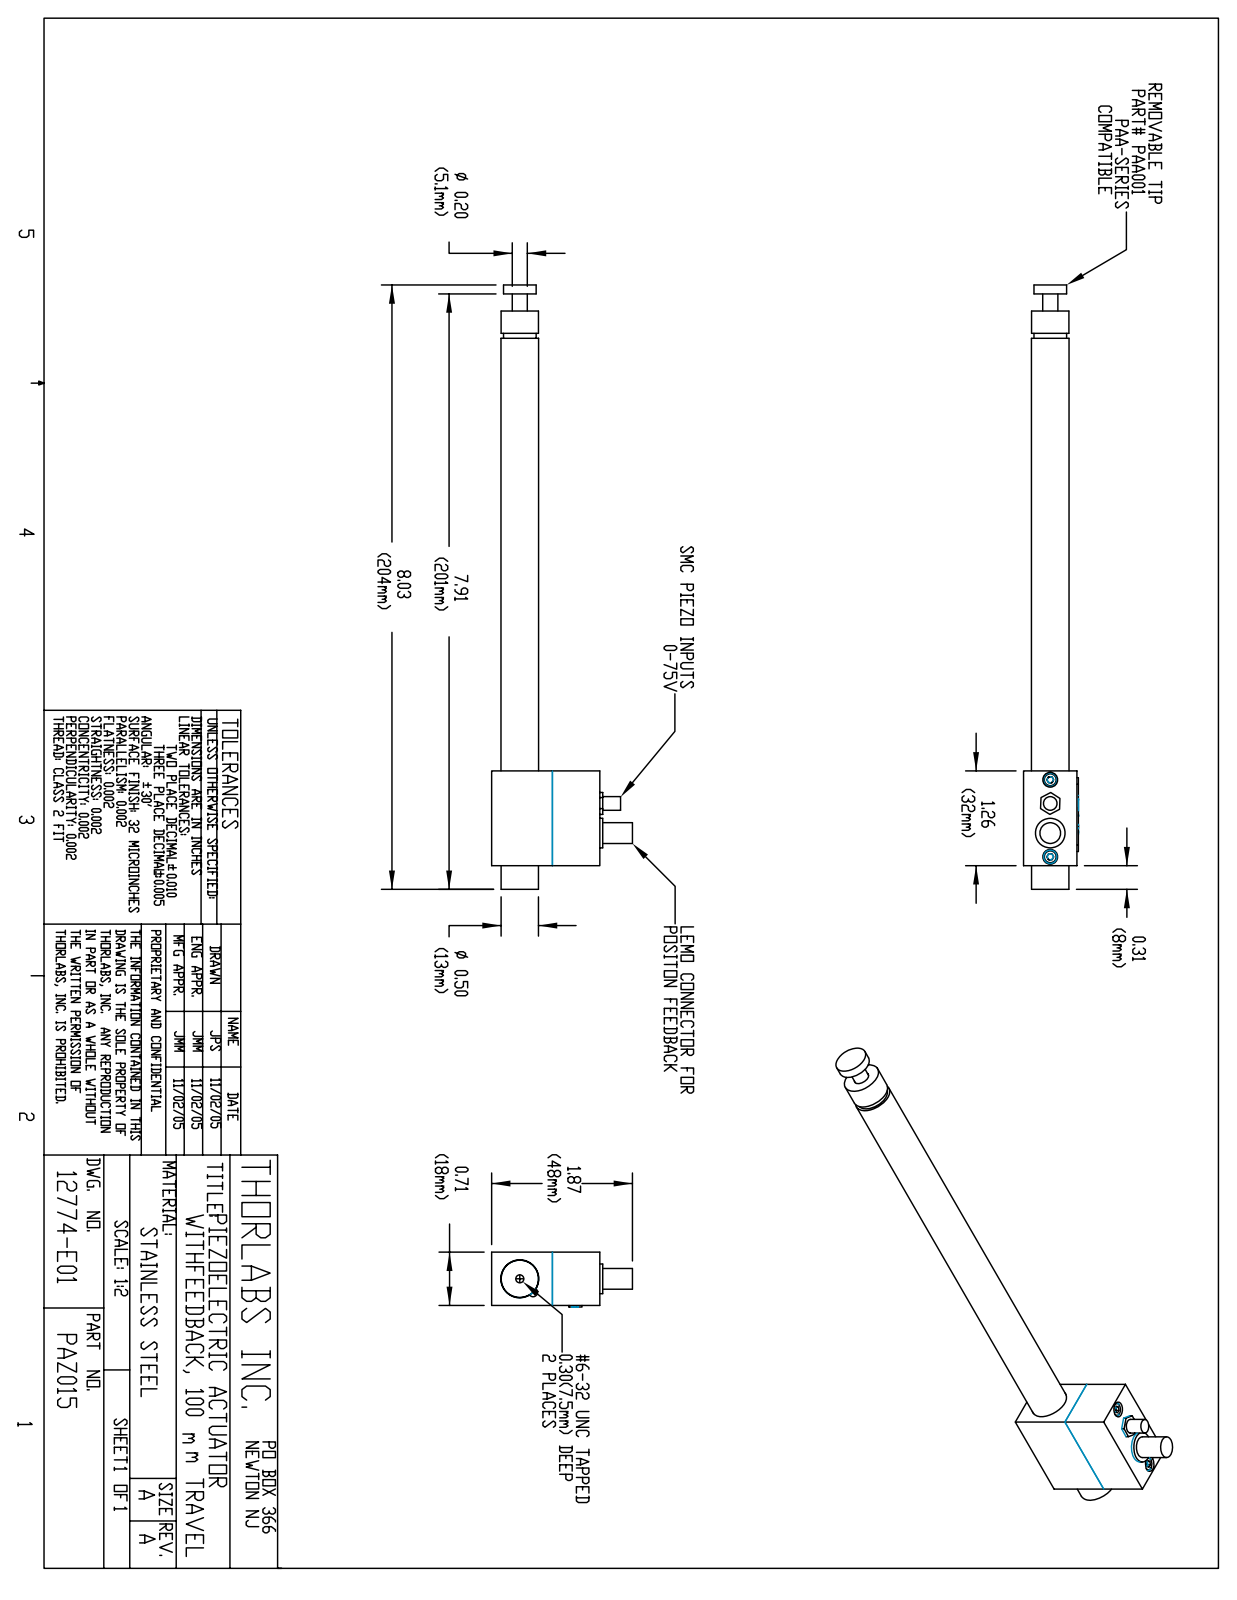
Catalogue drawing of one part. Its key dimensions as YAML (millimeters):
part_name: "12774-E0W"
step_written_by: "SolidWorks 2007 (AUTOMOTIVE_DESIGN)"
units: millimeters
bodies: {solids: 0, faces: 116, planar: 72, cylindrical: 36, other: 8}
overall_size: [204, 47.5, 18.5]
round_holes:
  - {diameter: 2.5, count: 2}
  - {diameter: 5, count: 2}
  - {diameter: 2.7, count: 1}
  - {diameter: 12.8, count: 1}
round_bosses_or_shafts:
  - {diameter: 12.7, count: 1}
  - {diameter: 12.6, count: 1}
  - {diameter: 11, count: 1}
  - {diameter: 10, count: 1}
  - {diameter: 7, count: 1}
  - {diameter: 5.1, count: 1}
  - {diameter: 4.6, count: 1}
partial_cylinders:
  - {radius: 2.2, count: 2}
  - {radius: 1.5, count: 1}
face_to_face_distances: [18, 32, 36.5, 40, 8, 0.5, 155.2, 187.2, 195.2, 18.5]
hole_center_spacings: [26]
